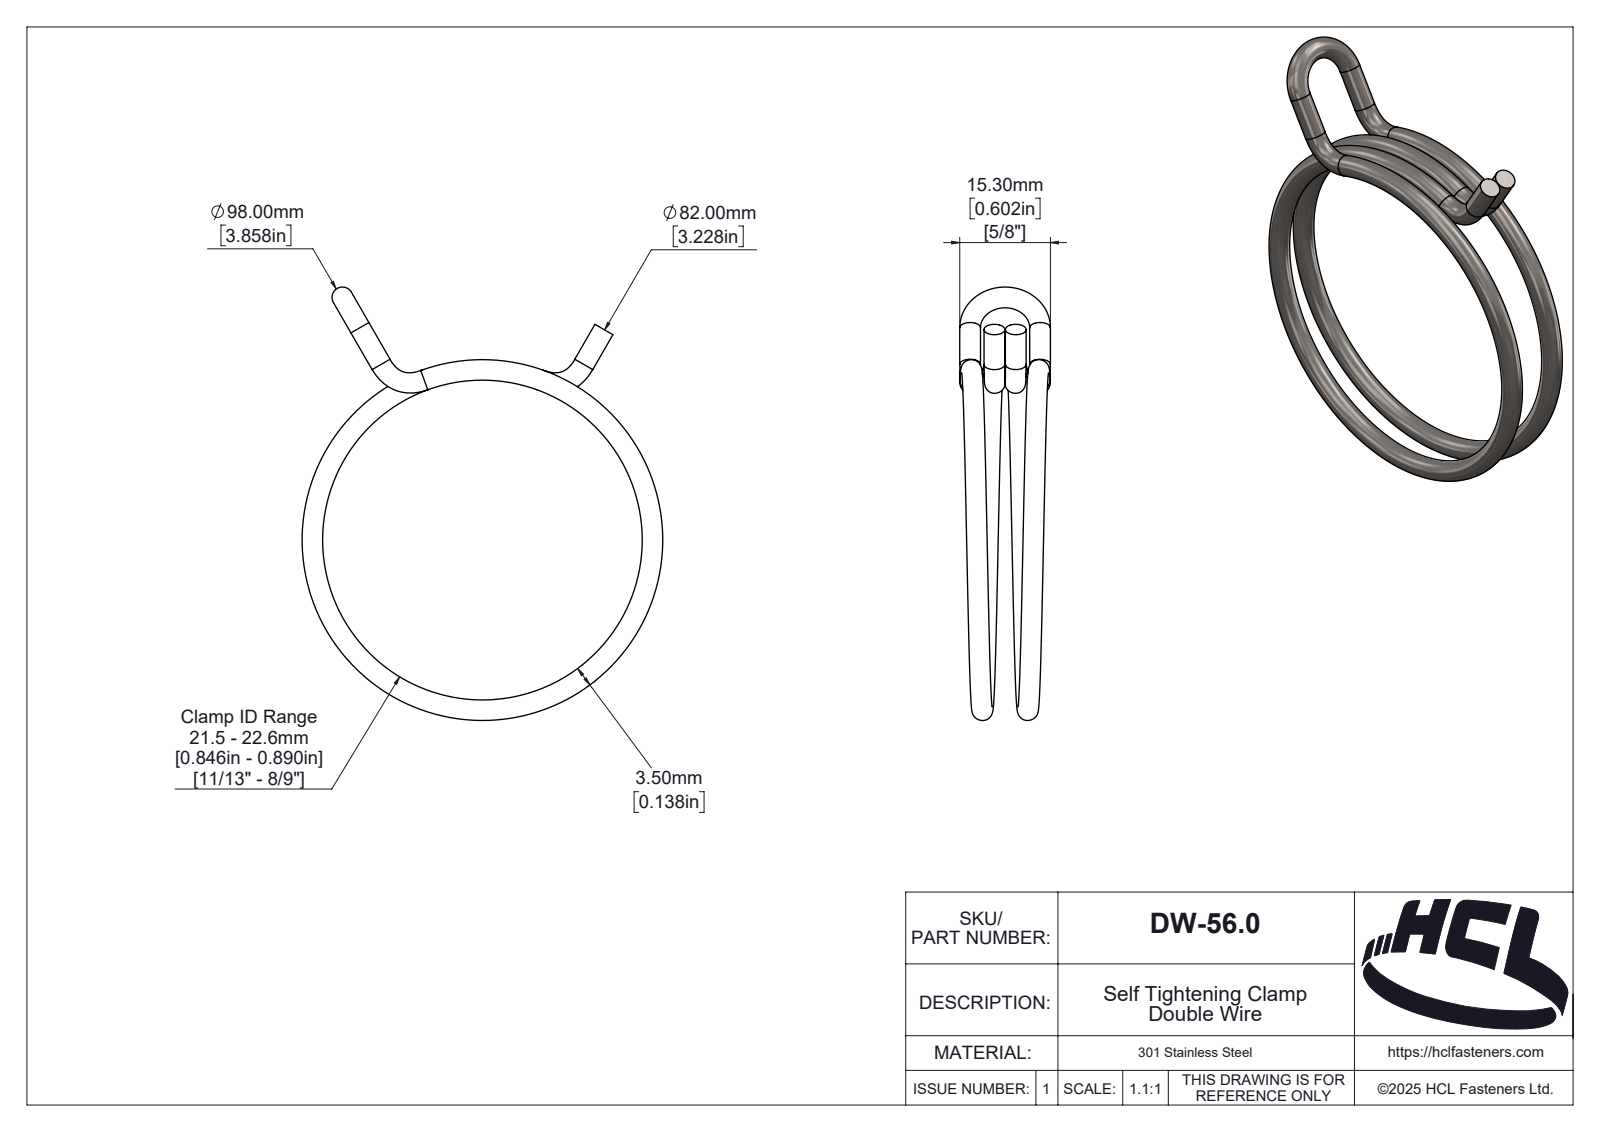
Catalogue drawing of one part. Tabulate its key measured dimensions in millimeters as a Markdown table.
| quantity | value |
| --- | --- |
| part name | DW-56.0 |
| STEP written by | SolidWorks 2025 (AUTOMOTIVE_DESIGN) |
| units | millimeters |
| bodies | 1 solid, 132 faces (14 planar, 53 cylindrical, 65 other) |
| overall size | 73.1 × 60.86 × 15.3 |
| volume | 4 565 mm³ |
| surface area | 5 275 mm² |
| round bosses / shafts (diameter × count) | 3.5 × 4 |
| partial cylindrical surfaces (radius × count) | 0.16 × 1, 0.2 × 1, 0.21 × 1, 0.26 × 1, 0.36 × 1, 0.48 × 1, 0.6 × 1, 0.68 × 1 |
